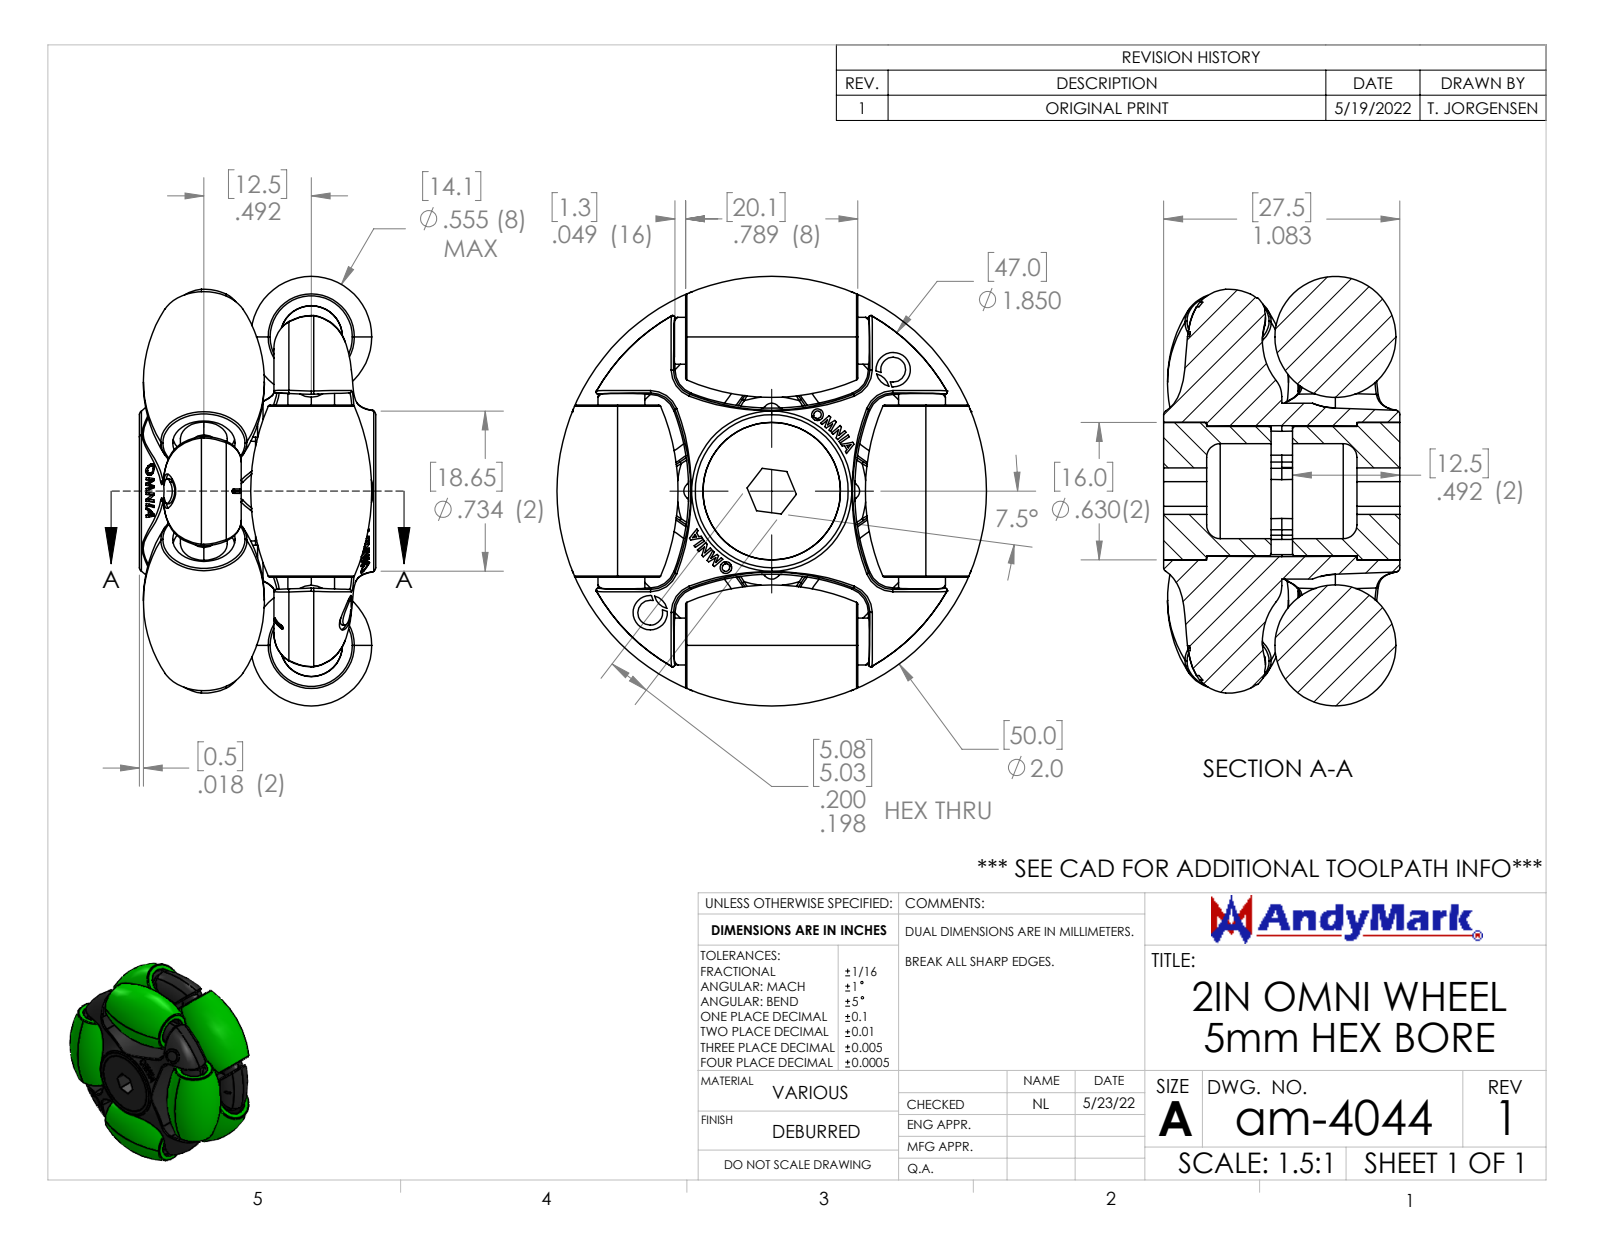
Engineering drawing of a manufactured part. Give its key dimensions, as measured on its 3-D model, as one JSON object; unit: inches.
{"part_name": "2in Omni 14mm Hex; am-4044 2in Omni Wheel 5mm Hex Bore; am-3909 14mm Hex to 5mm Hex", "step_written_by": "SolidWorks 2021 (CONFIG_CONTROL_DESIGN)", "units": "inches", "bodies": {"solids": 3, "faces": 1083, "planar": 314, "cylindrical": 147, "other": 622}, "overall_size": [1.968, 1.968, 1.083], "volume_in3": 1.994, "surface_area_in2": 26.92, "round_holes": [[0.157, 4], [0.435, 1], [0.63, 1]], "round_bosses_or_shafts": [[0.214, 6], [0.114, 4], [0.214, 2]], "partial_cylinders_radius": [[0.01, 12], [0.008, 8], [0.028, 6], [0.027, 4], [0.033, 4], [0.079, 4], [0.092, 4], [0.291, 1]], "face_to_face_distances": [0.547, 0.197, 1.083, 0.789, 0.046, 0.743, 0.344, 0.541, 0.886, 0.175], "hole_center_spacings": [0.787, 1.455, 0.602, 0.603, 1.575, 1.575]}
